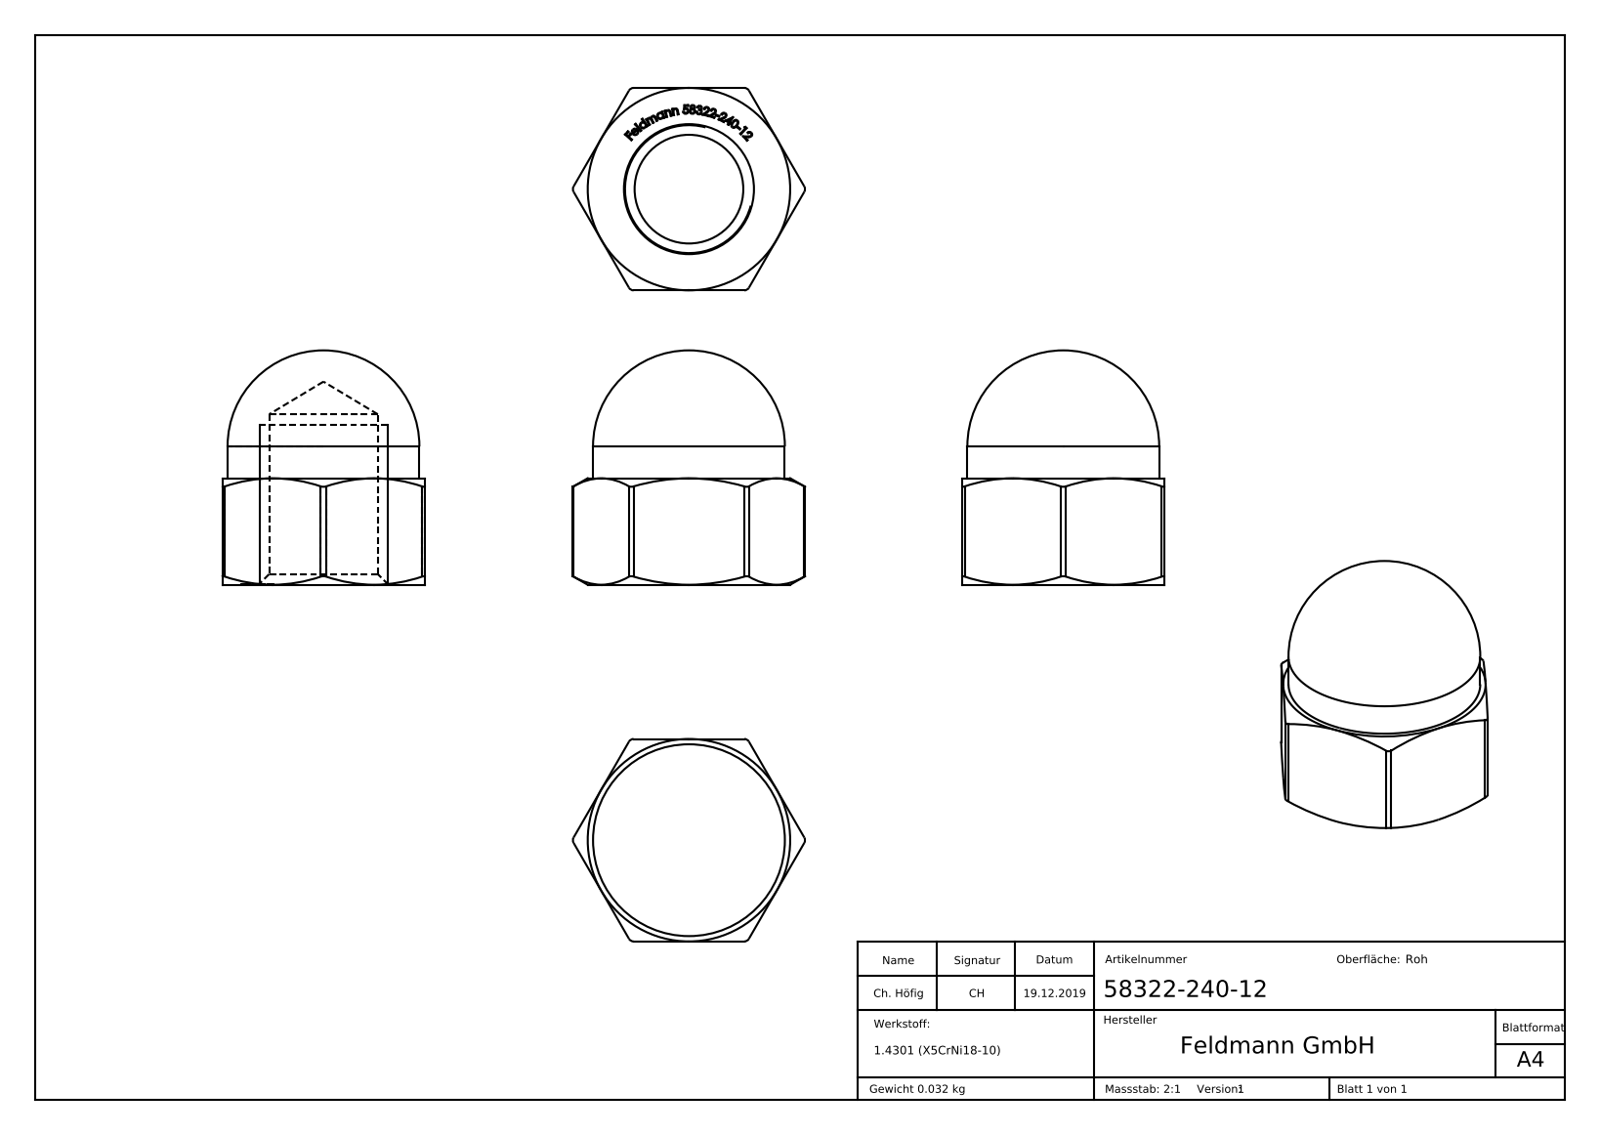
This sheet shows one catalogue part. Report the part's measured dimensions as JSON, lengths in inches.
{"part_name": "58322-240-12", "step_written_by": "SolidWorks 2015 (CONFIG_CONTROL_DESIGN)", "units": "inches", "bodies": {"solids": 1, "faces": 31, "planar": 8, "cylindrical": 8, "other": 15}, "overall_size": [1.063, 0.858, 0.748], "volume_in3": 0.244, "surface_area_in2": 3.385, "round_holes": [[0.402, 1]], "round_bosses_or_shafts": [[0.709, 1]], "partial_cylinders_radius": [[0.02, 6]], "face_to_face_distances": [0.748, 0.394]}
